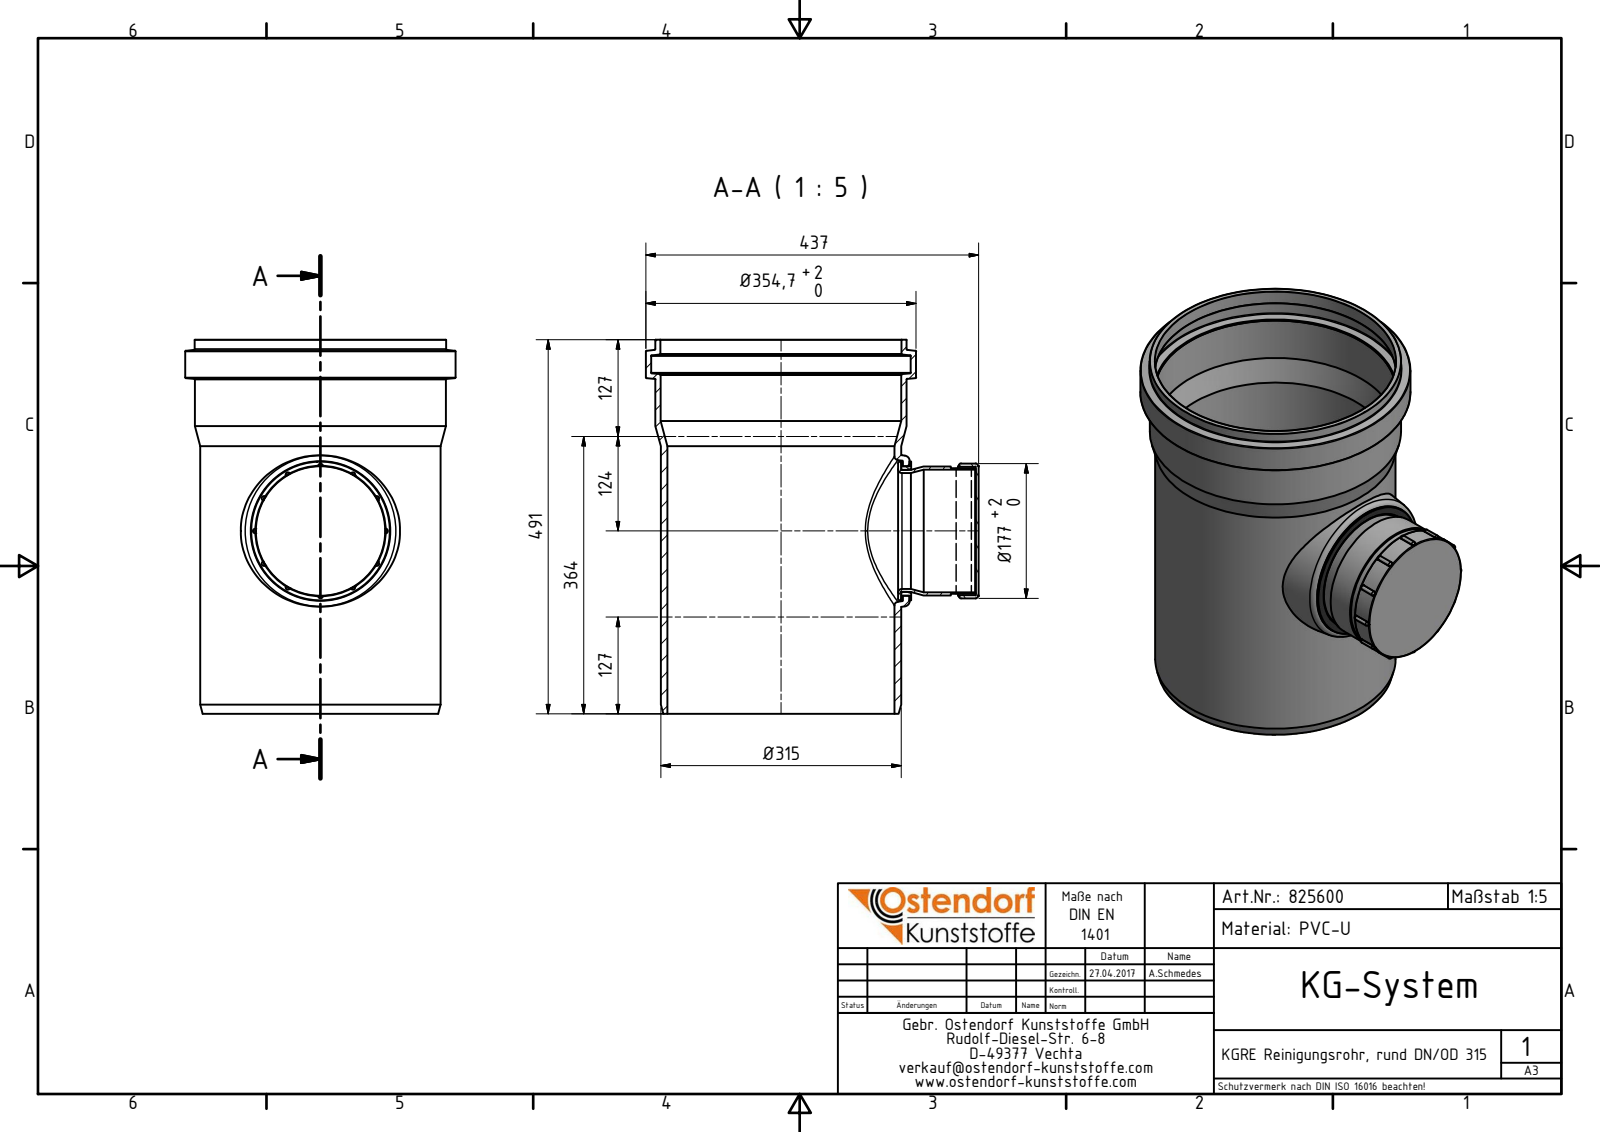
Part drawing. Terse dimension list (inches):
name: 825600 KGRE Reinigungsrohr, rund DN_OD 315; 825600 KGRE Reinigungsrohr, rund DN_OD 315 Dichtung; 825600 KGRE Reinigungsrohr, rund DN_OD 315 Abzweig; 825600 KGRE Reinigungsrohr, rund DN_OD 315 Deckel
written by: Autodesk Inventor 2016 (AUTOMOTIVE_DESIGN)
unit: in
bodies: 4 solids, 208 faces (64 planar, 92 cylindrical, 52 other)
size: 19.802 × 17.205 × 13.965
volume: 267.9 in³; area: 1 905 in²
holes: 1× ⌀5.984, 1× ⌀6.299, 1× ⌀6.339, 1× ⌀6.496, 1× ⌀6.693, 1× ⌀11.74, 1× ⌀12.441, 1× ⌀12.453, 1× ⌀13.421
bosses: 1× ⌀13.965, 1× ⌀12.996, 1× ⌀12.984, 1× ⌀12.425, 1× ⌀7.165, 1× ⌀6.732, 1× ⌀6.654
rounds: 40× R0.116, 12× R0.118
face distances: 0.157, 4.01, 0.079, 0.433, 3.852, 3.774, 3.931, 0.354, 3.419, 3.577
